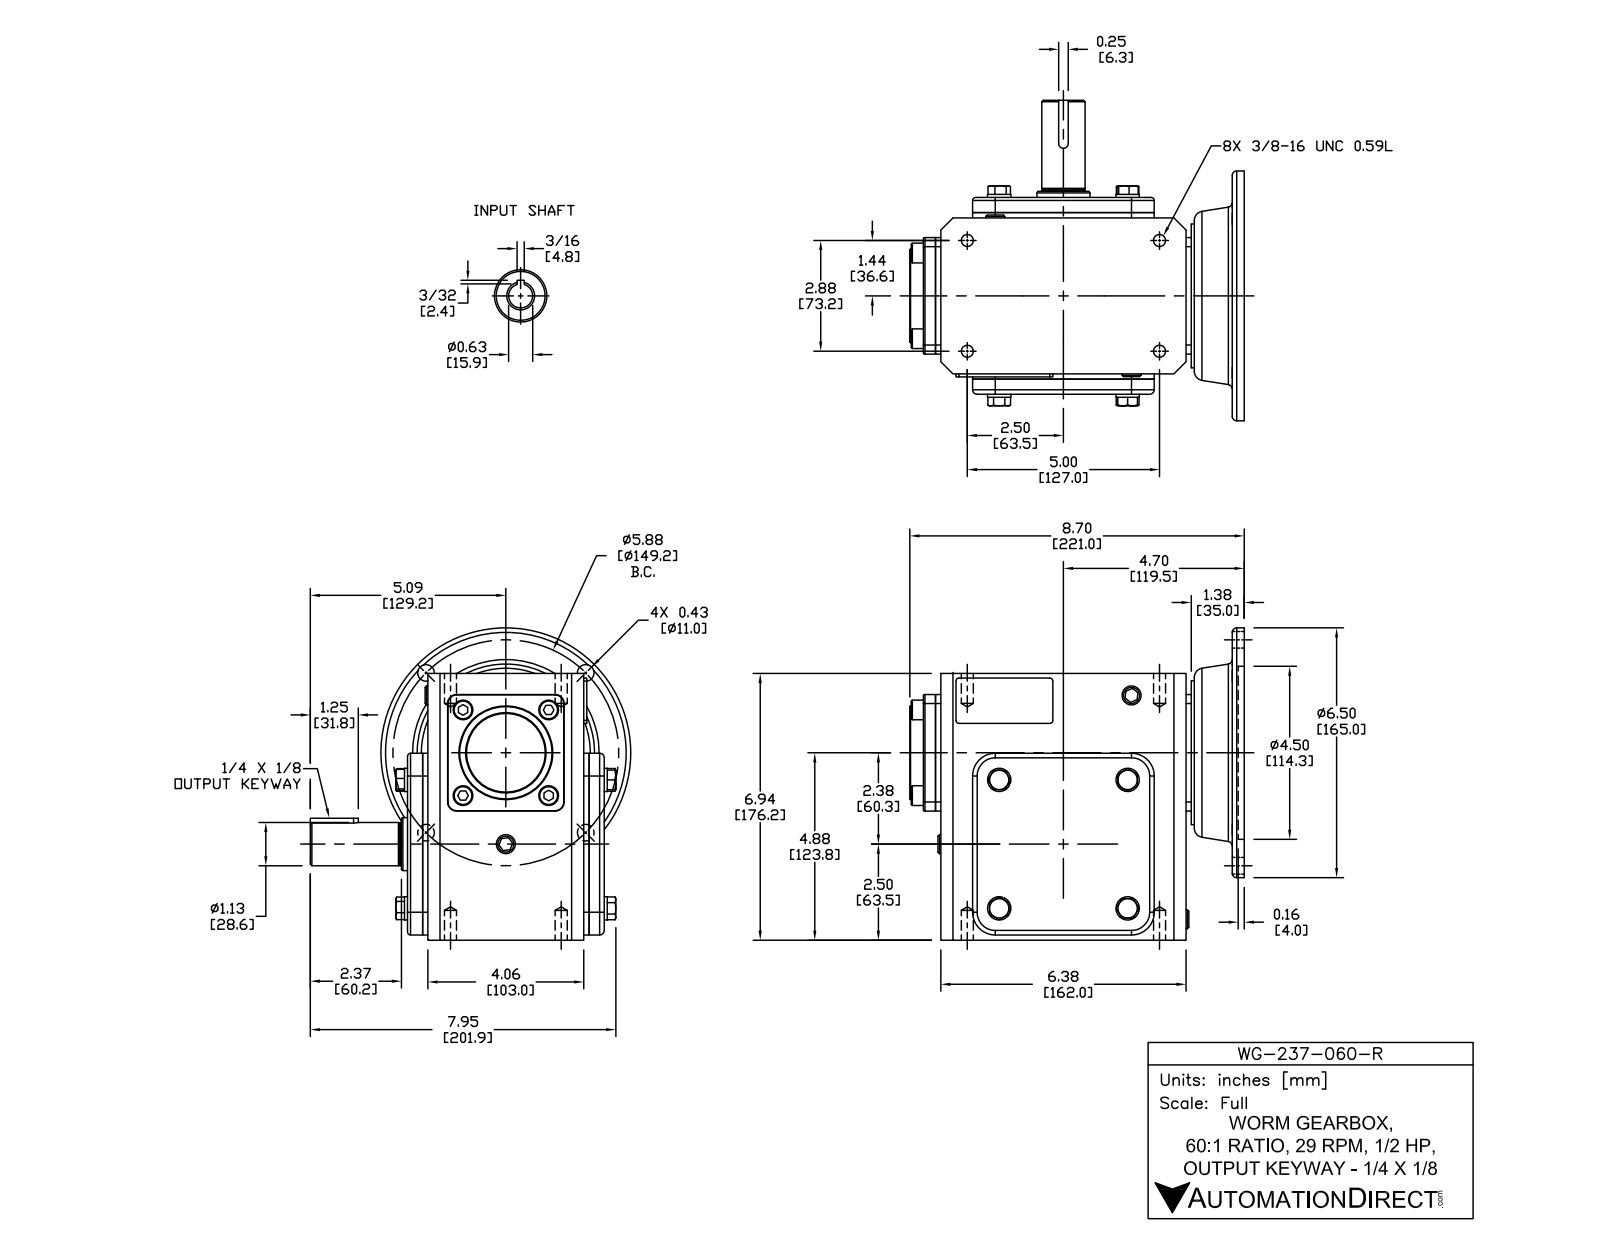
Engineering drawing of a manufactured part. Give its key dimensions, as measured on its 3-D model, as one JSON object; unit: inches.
{"part_name": "WG-237-060-R", "step_written_by": "SolidWorks 2015 (CONFIG_CONTROL_DESIGN)", "units": "inches", "bodies": {"solids": 37, "faces": 537, "planar": 294, "cylindrical": 153, "other": 90}, "overall_size": [8.701, 8.335, 8.123], "volume_in3": 222.4, "surface_area_in2": 508.3, "round_holes": [[0.313, 4], [0.406, 4], [0.591, 1], [0.625, 1], [1.378, 1], [1.457, 1], [1.772, 1], [3.819, 1], [4.5, 1]], "round_bosses_or_shafts": [[0.606, 4], [0.512, 4], [6.496, 1], [3.74, 1], [2.441, 1], [2.047, 1], [1.181, 1], [1.142, 1]], "partial_cylinders_radius": [[0.079, 12], [0.236, 6], [0.118, 4], [0.591, 4], [0.02, 2], [0.039, 2], [0.125, 1]], "face_to_face_distances": [0.138, 4.724, 0.394, 4.331, 0.531, 4.587, 4.193, 6.516, 6.937, 0.315], "hole_center_spacings": [2.937, 2.098, 2.88, 4.154, 4.154, 4.913, 5, 5.77]}
